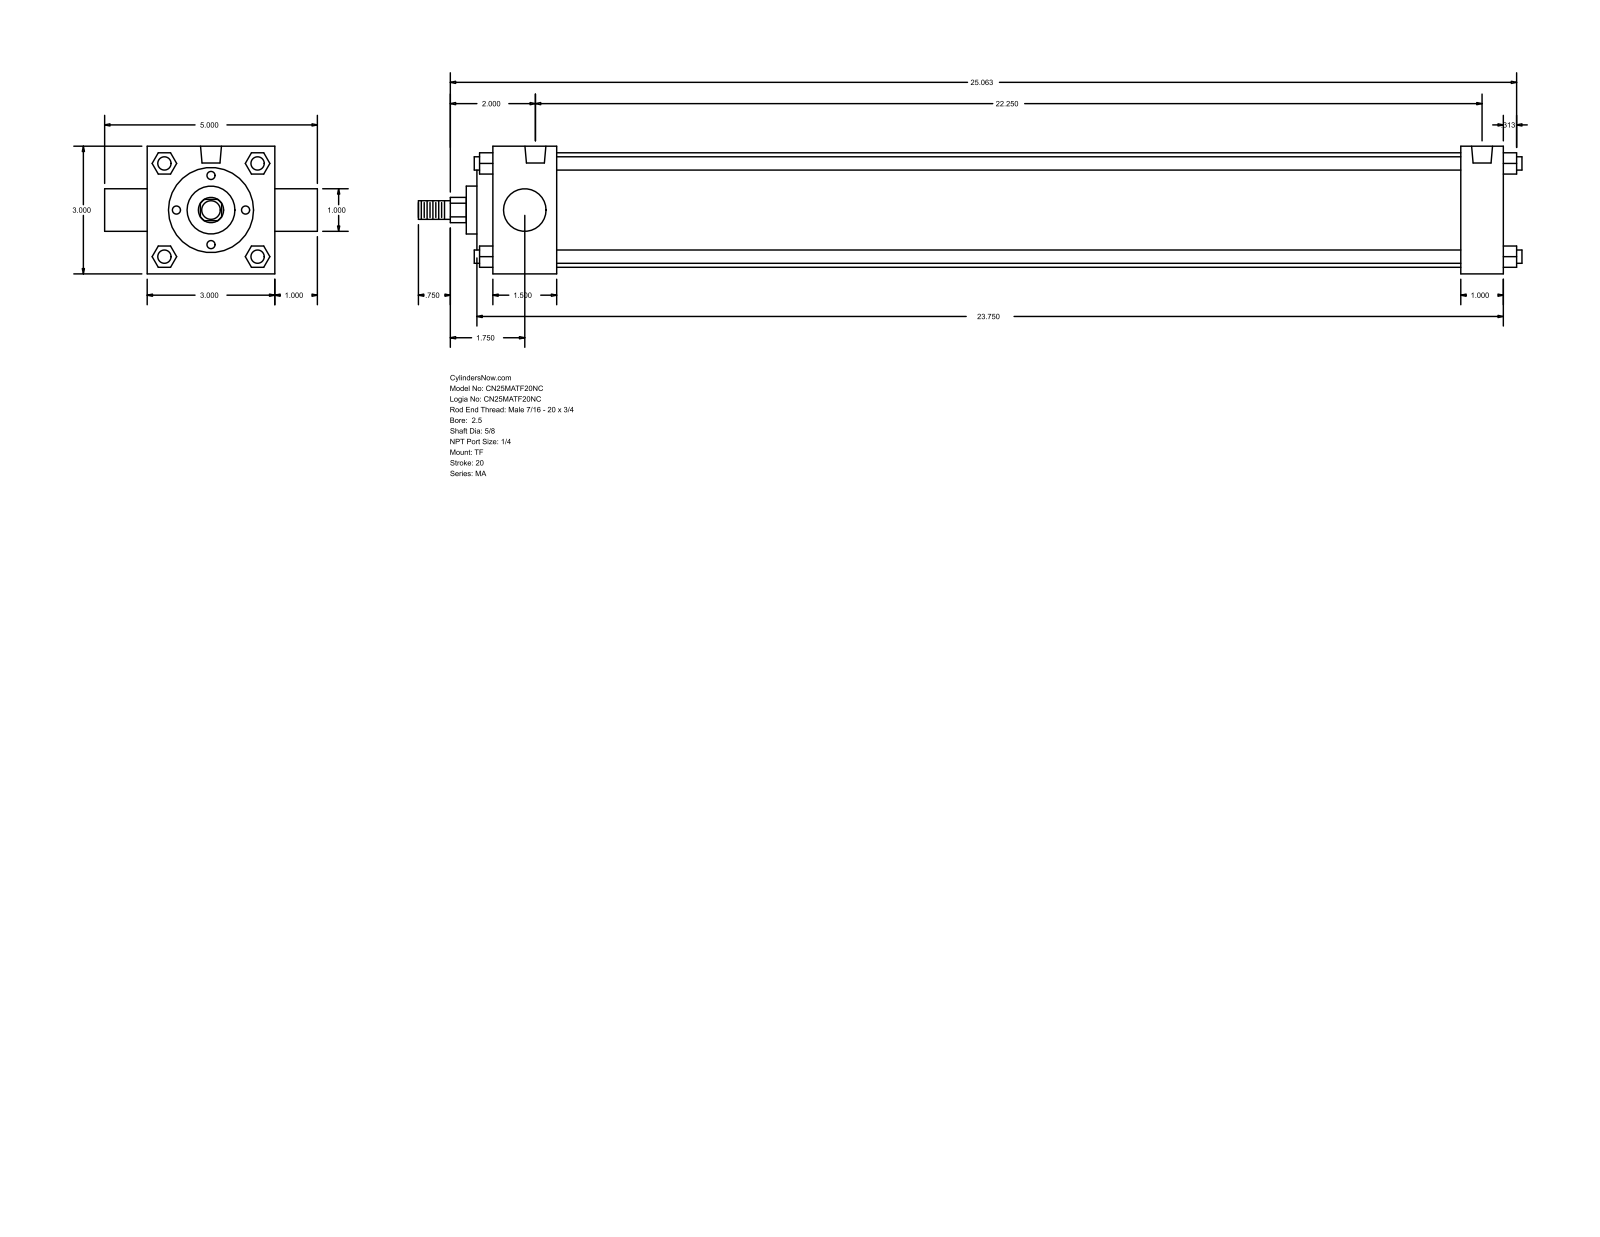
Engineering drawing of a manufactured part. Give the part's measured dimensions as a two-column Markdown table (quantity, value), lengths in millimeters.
| quantity | value |
| --- | --- |
| part name | MA_TF__0250_0.625 |
| STEP written by | GSSL Pune (CONFIG_CONTROL_DESIGN) |
| units | millimeters |
| bodies | 0 solids, 122 faces (93 planar, 29 cylindrical, 0 other) |
| overall size | 658.81 × 127 × 76.2 |
| round holes (diameter × count) | 7.94 × 3, 12.49 × 2 |
| round bosses / shafts (diameter × count) | 7.94 × 4, 68.33 × 1, 50.8 × 1, 28.57 × 1, 25.4 × 1, 15.88 × 1, 11.11 × 1 |
| partial cylindrical surfaces (radius × count) | 7.54 × 1 |
| main face-to-face distances | 76.2, 603.25, 25.4, 38.1, 577.85, 539.75, 565.15, 12.7, 9.52, 47.62 |
| hole center spacings | 565.15 |
